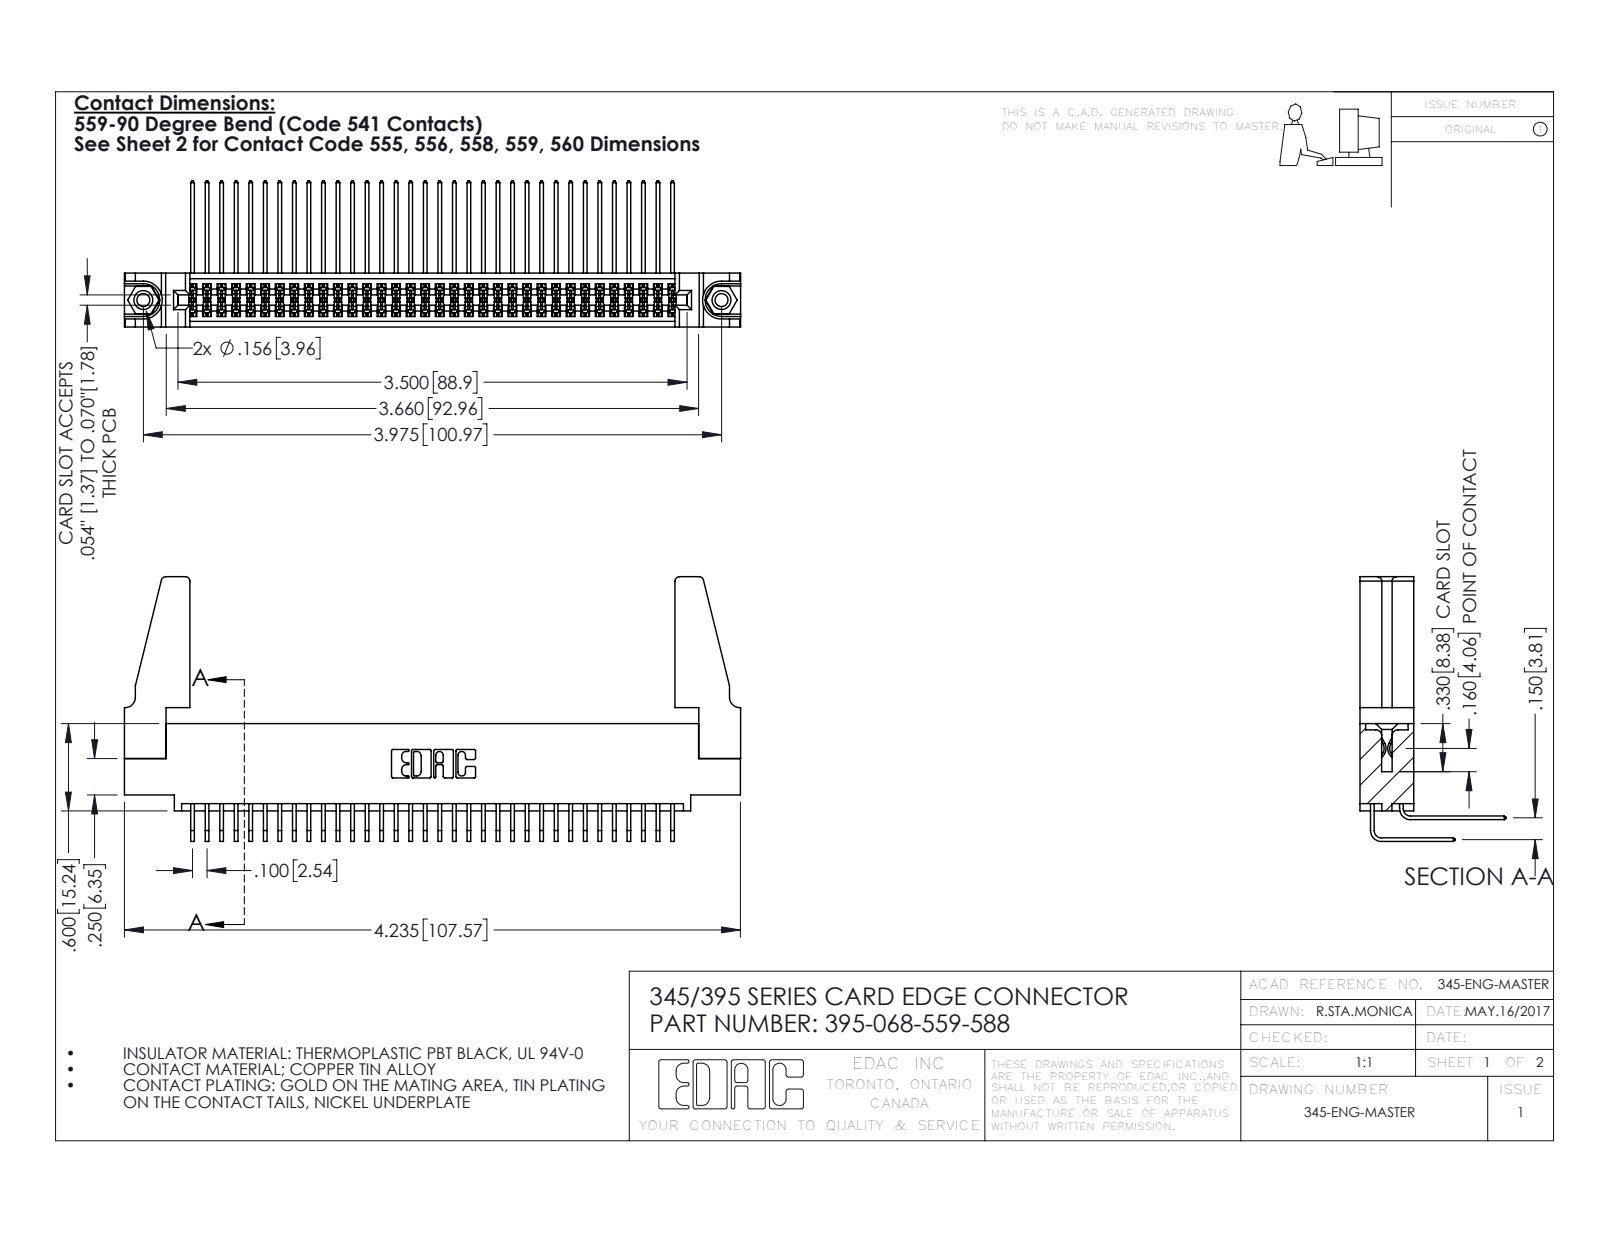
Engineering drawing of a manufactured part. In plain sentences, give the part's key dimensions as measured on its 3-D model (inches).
The part is named "345-292-001_558 559 Tail - 1; 345-250-001_345-250-001-102; 345 Part_0.110 Offset - 0.156 Dia-TH; 345-220-078_345-220-088 (+2 more)". Its 3-D file was written by "SolidWorks 2016 (CONFIG_CONTROL_DESIGN)". It is 73 solids with 3790 faces: 2536 planar, 1238 cylindrical and 16 other. Overall it measures 4.236 by 1.819 by 1.005 inches. Its volume is 0.851 cubic inches and its surface area 32.11 square inches. Round holes: 2 of diameter 0.089, 2 of diameter 0.125, 2 of diameter 0.156, 1 of diameter 0.064. Round bosses or shafts: 2 of diameter 0.155. Partial cylindrical surfaces (rounded edges, fillets, slot ends): 103 of radius 0.006, 22 of radius 0.01, 8 of radius 0.03, 6 of radius 0.007, 6 of radius 0.031, 3 of radius 0.026, 2 of radius 0.014, 2 of radius 0.019. The main face-to-face distances are 0.072, 0.298, 0.37, 0.2, 0.098, 0.272, 0.025, 0.225, 0.175, 0.15. The hole center spacings are 0.27, 3.74, 3.975.
